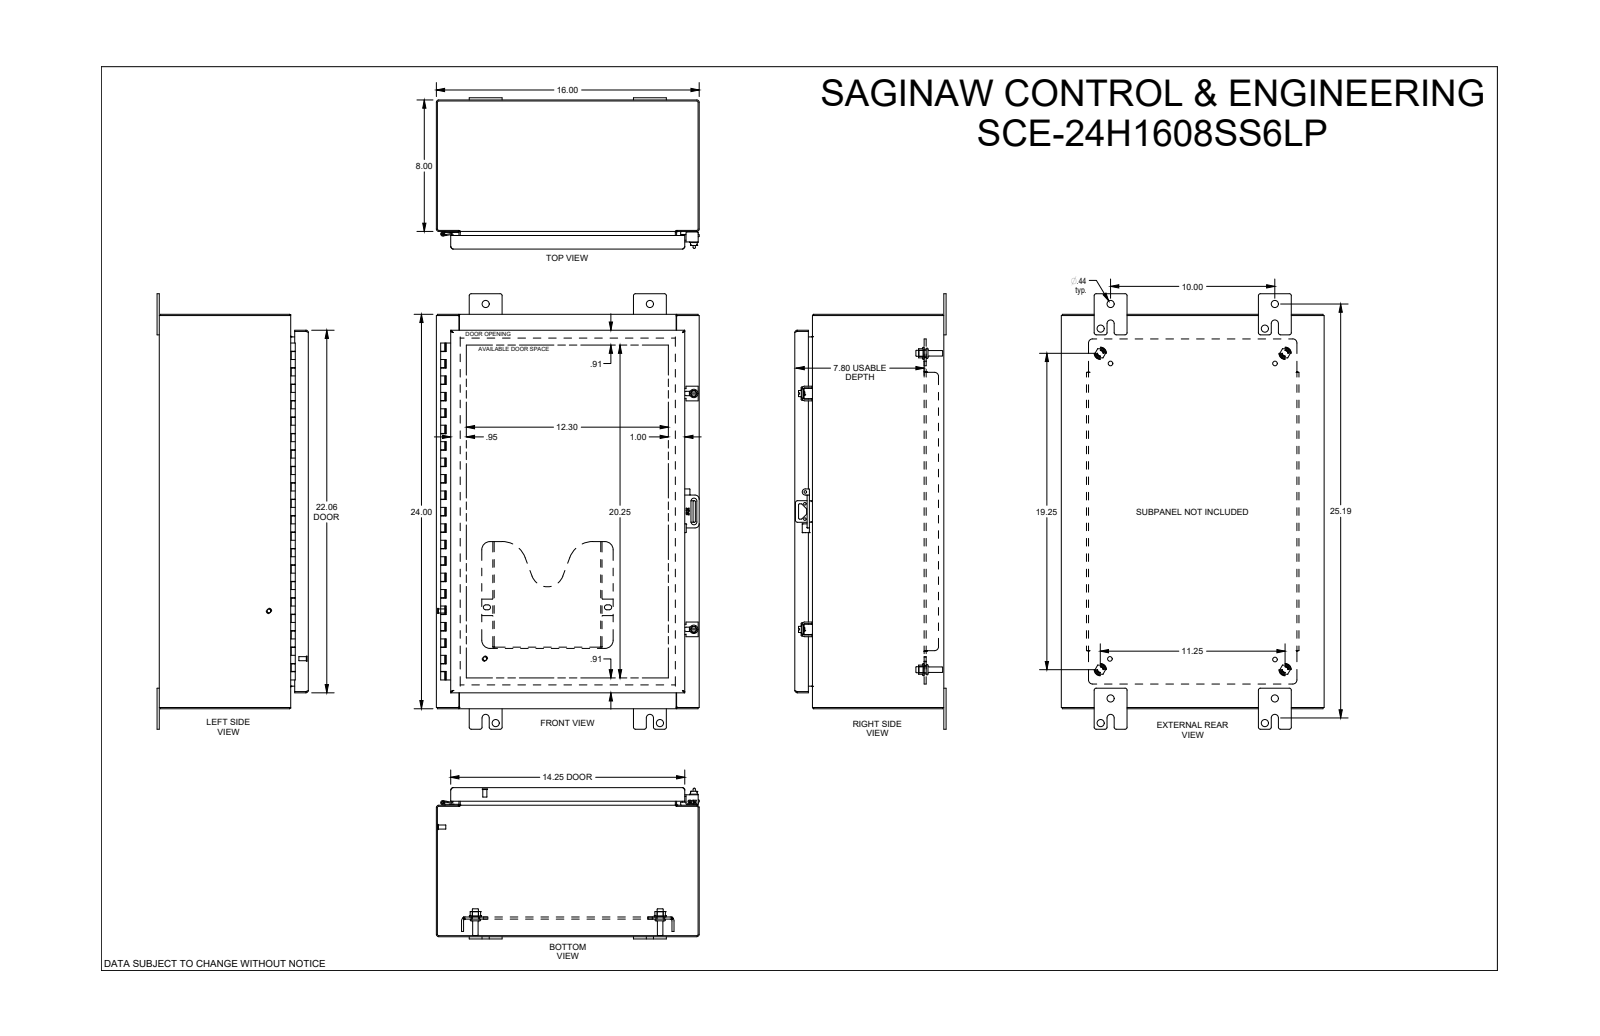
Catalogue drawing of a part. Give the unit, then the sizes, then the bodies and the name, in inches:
Units: inches
Overall size (bounding box): 26.5 × 16 × 9.208
Round holes (diameter × count): ⌀0.437 ×8, ⌀0.25 ×5, ⌀0.19 ×4, ⌀0.193 ×4, ⌀0.281 ×4, ⌀0.367 ×4, ⌀0.5 ×4, ⌀0.16 ×2, ⌀0.203 ×2, ⌀0.13 ×1, ⌀0.132 ×1
Round bosses / shafts (diameter × count): ⌀0.248 ×7, ⌀0.563 ×5, ⌀0.366 ×4, ⌀0.332 ×4, ⌀0.256 ×4, ⌀0.188 ×4, ⌀0.25 ×3, ⌀0.507 ×2
Partial cylindrical surfaces — rounded edges, fillets, slot ends (radius × count): R0.01 ×114, R0.015 ×36, R0.029 ×30, R0.03 ×27, R0.125 ×27, R0.06 ×25, R0.04 ×22, R0.07 ×14
Main face-to-face distances: 0.075, 15.925, 0.075, 8.998, 8.923, 8.998, 9.073, 7.923, 1.2, 1.125
Hole centre spacings: 10, 0.875, 6.5, 10.65, 18.641, 21.451, 0.515, 1.439
Bodies: 0 solids, 3160 faces (1275 planar, 660 cylindrical, 1225 other)
Part name (STEP PRODUCT): SCE-24H1608SS6LP
STEP written by: SolidWorks 2019 (CONFIG_CONTROL_DESIGN)
